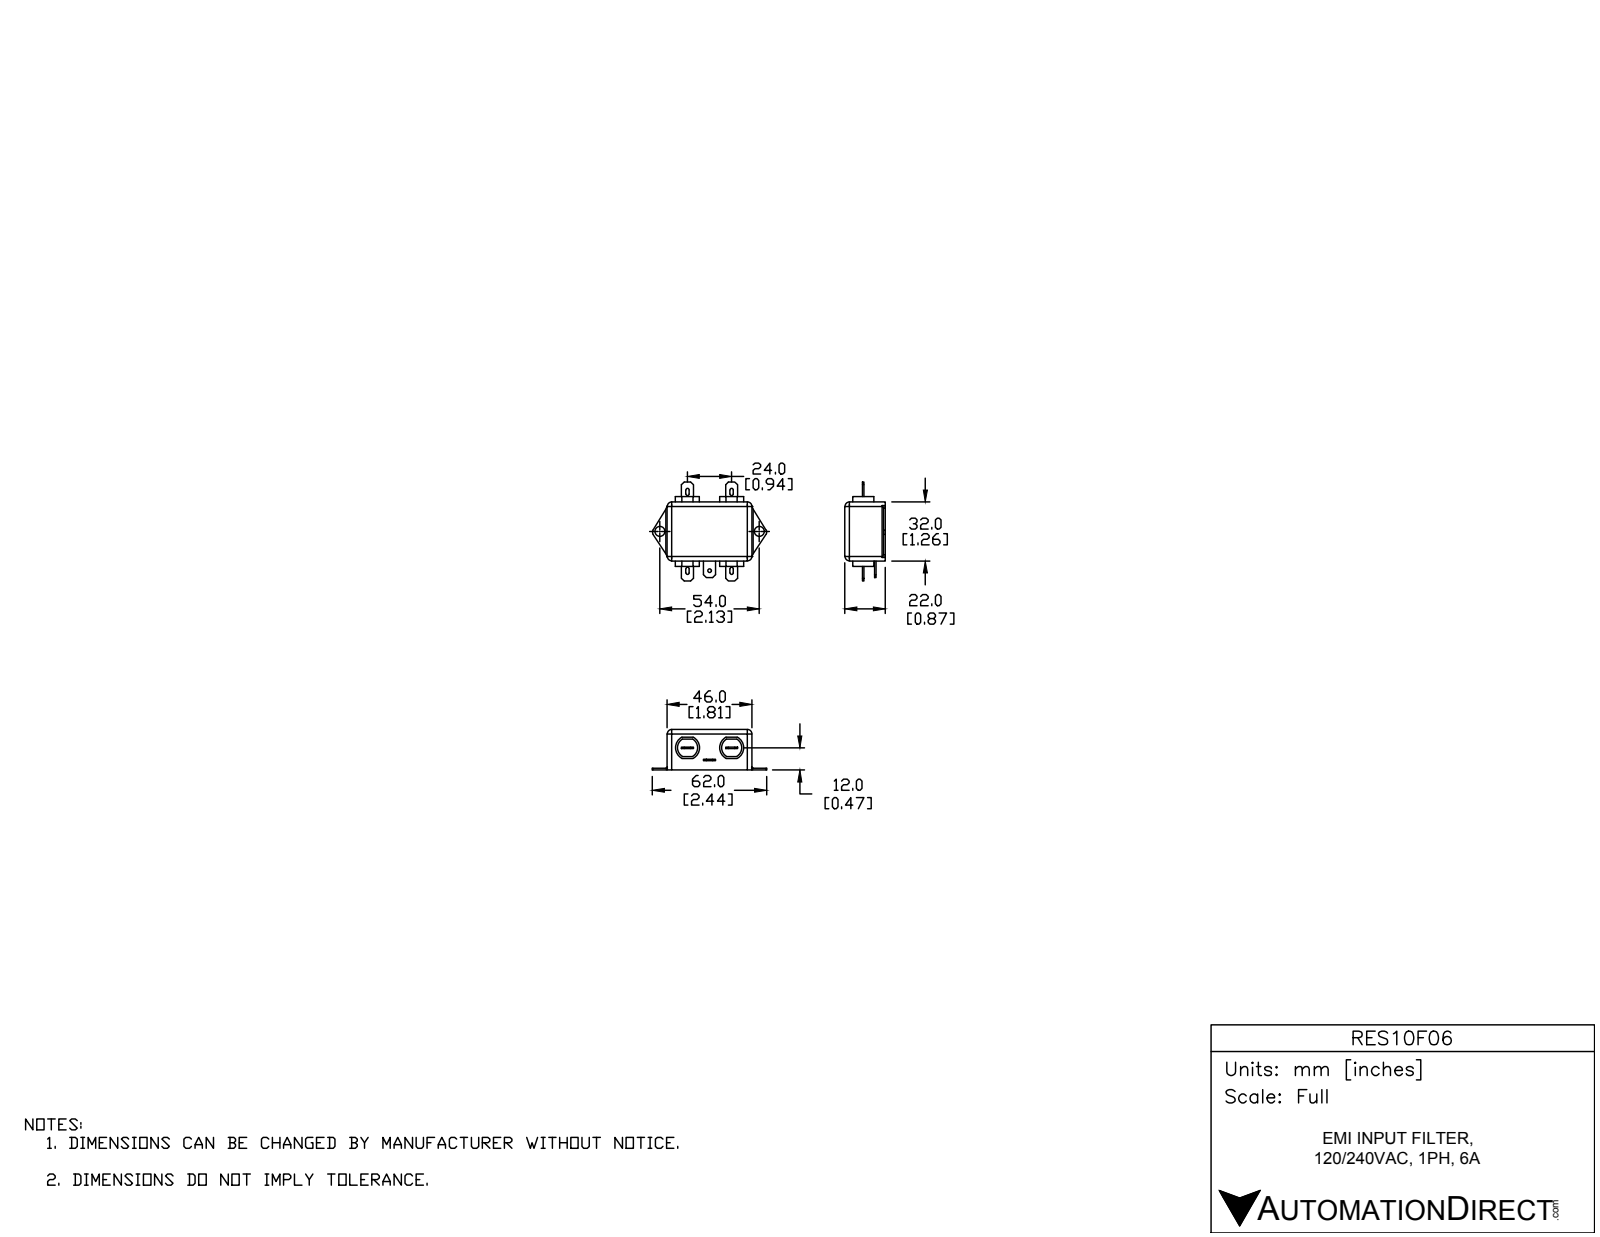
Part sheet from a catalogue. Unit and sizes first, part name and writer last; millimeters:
Units: millimetres
Overall size (bounding box): 61.3 × 56.1 × 22
Round holes (diameter × count): ⌀5.3 ×2, ⌀2 ×1
Partial cylindrical surfaces — rounded edges, fillets, slot ends (radius × count): R2.5 ×10, R0.9 ×8, R0.5 ×4, R0.75 ×2, R5.5 ×2, R6.5 ×2
Main face-to-face distances: 22, 34.3, 46, 1.4, 35.7, 0.8, 1, 11.6, 12.4, 10.4
Hole centre spacings: 35.11, 54
Volume: 35 744 mm³ · Surface area: 8 153 mm²
Bodies: 1 solid, 145 faces (79 planar, 58 cylindrical, 8 other)
Part name (STEP PRODUCT): RES10F06
STEP written by: SolidWorks 2015 (AUTOMOTIVE_DESIGN)
